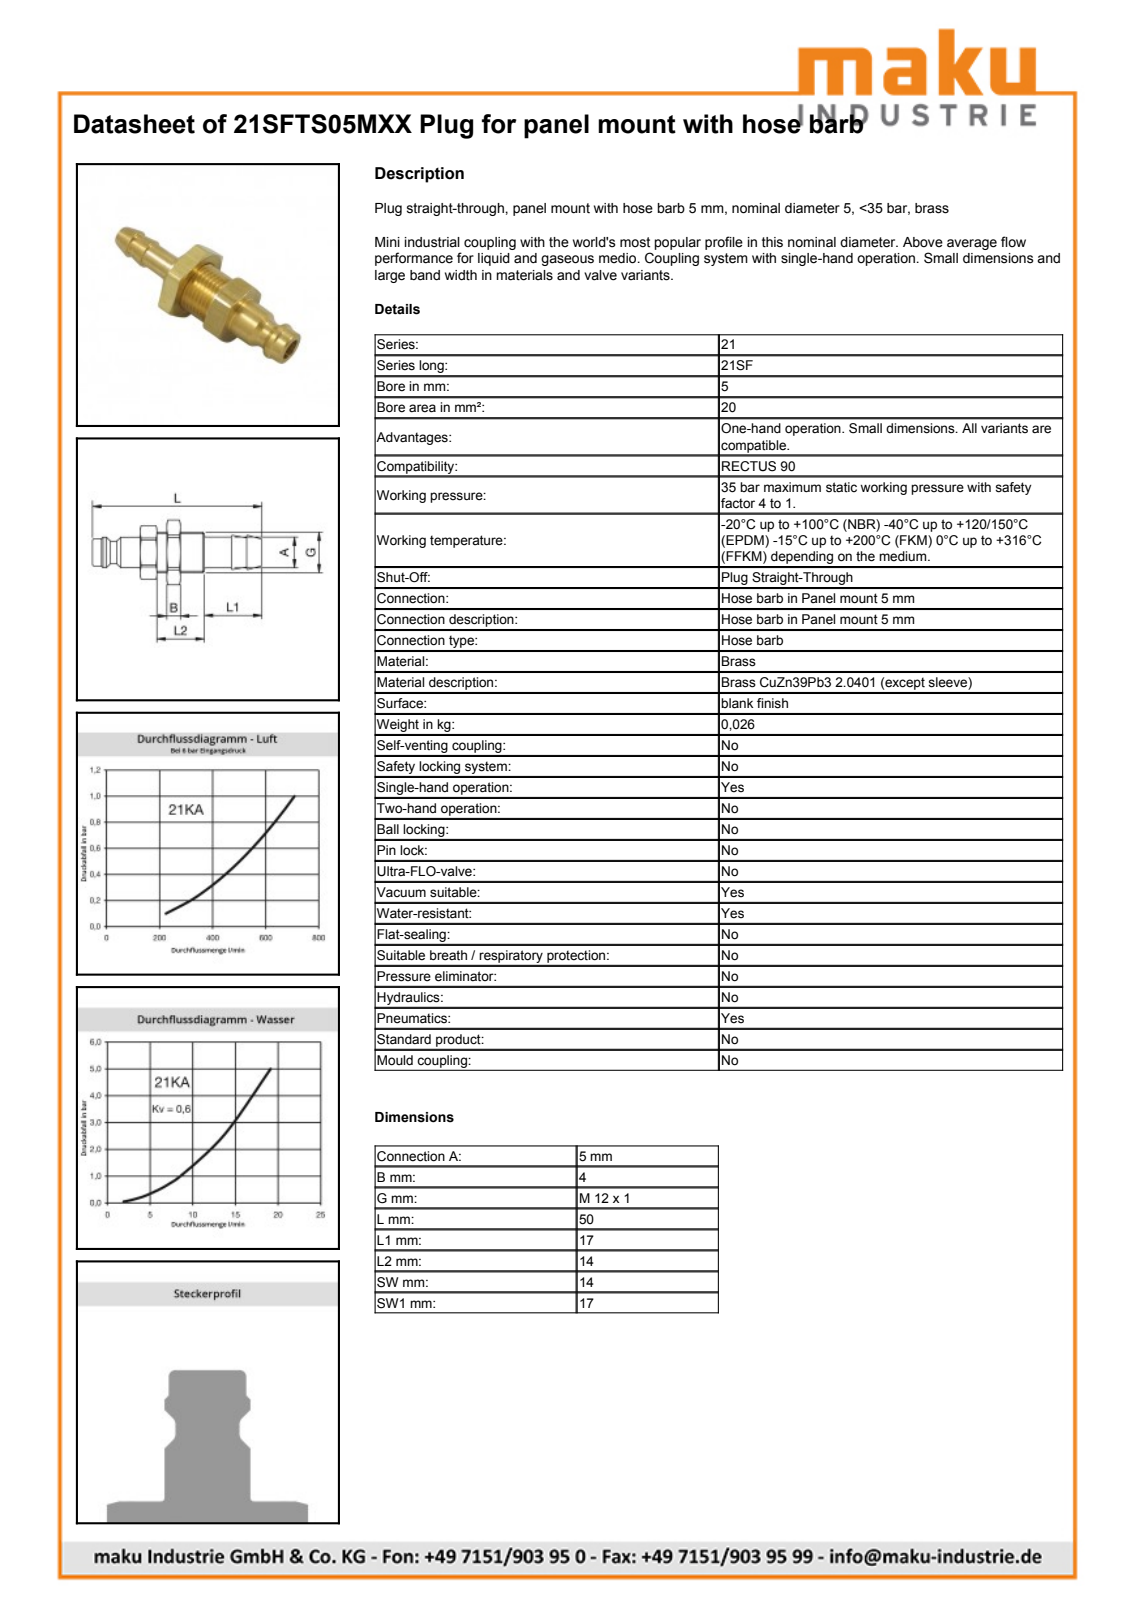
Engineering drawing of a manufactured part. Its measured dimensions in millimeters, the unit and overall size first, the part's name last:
Units: millimetres
Overall size (bounding box): 50 × 18.84 × 18.53
Round holes (diameter × count): ⌀3 ×1, ⌀4.95 ×1, ⌀12 ×1
Round bosses / shafts (diameter × count): ⌀10.6 ×1, ⌀9 ×1, ⌀8.1 ×1, ⌀6.65 ×1, ⌀5.05 ×1
Partial cylindrical surfaces — rounded edges, fillets, slot ends (radius × count): R7.9 ×1, R9.57 ×1
Main face-to-face distances: 14, 17, 4, 11.36, 7.36, 7.54, 11.54, 18.9, 6.46, 2.46
Volume: 3 329 mm³ · Surface area: 2 966 mm²
Bodies: 2 solids, 85 faces (21 planar, 22 cylindrical, 42 other)
Part name (STEP PRODUCT): D110760; D110759; D104296
STEP written by: Autodesk Inventor 2013 (AUTOMOTIVE_DESIGN)
